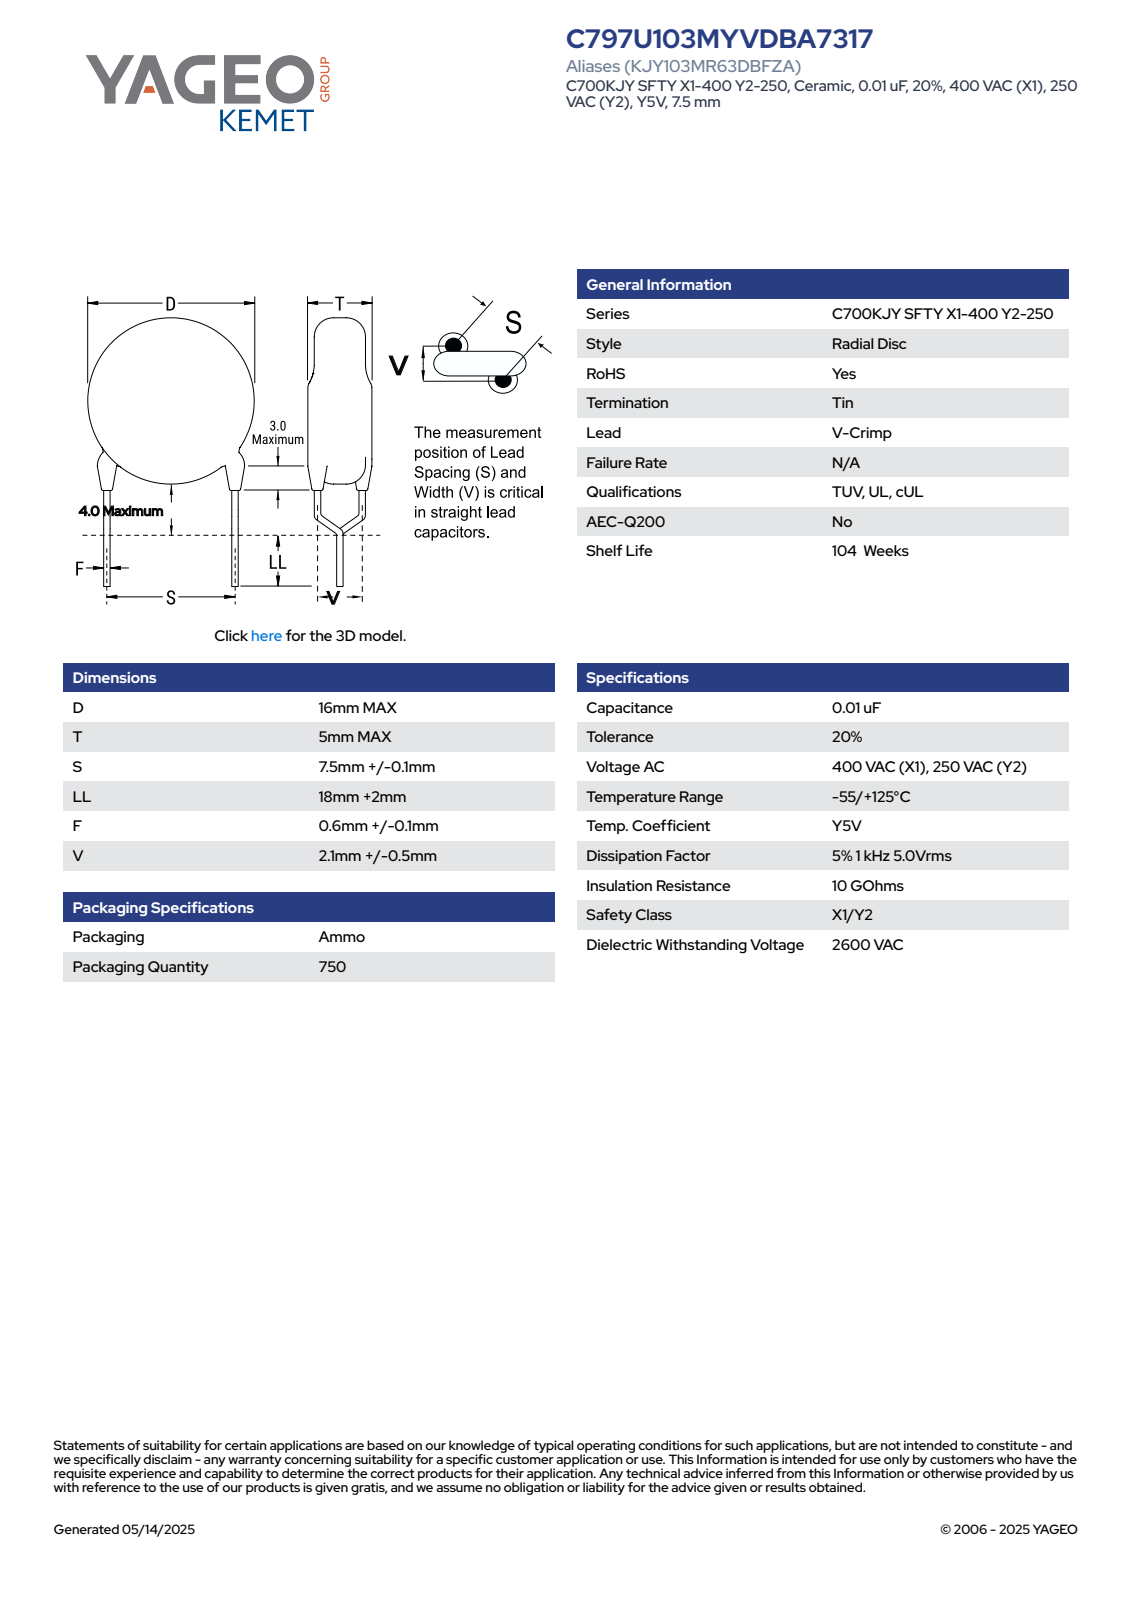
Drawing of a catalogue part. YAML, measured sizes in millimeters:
part_name: "CCD_VC16X5_D16T5S7.5LL20F0.7V2.1"
step_written_by: "SolidWorks 2021 (AUTOMOTIVE_DESIGN)"
units: millimeters
bodies: {solids: 4, faces: 85, planar: 63, cylindrical: 18, other: 4}
overall_size: [36, 16, 5]
volume: 1002
surface_area: 729
round_bosses_or_shafts:
  - {diameter: 0.7, count: 6}
  - {diameter: 1.2, count: 2}
  - {diameter: 16, count: 1}
face_to_face_distances: [5, 20, 29.26, 9.26, 27.33, 7.33, 1.93, 0.53, 0.36, 7.92]
